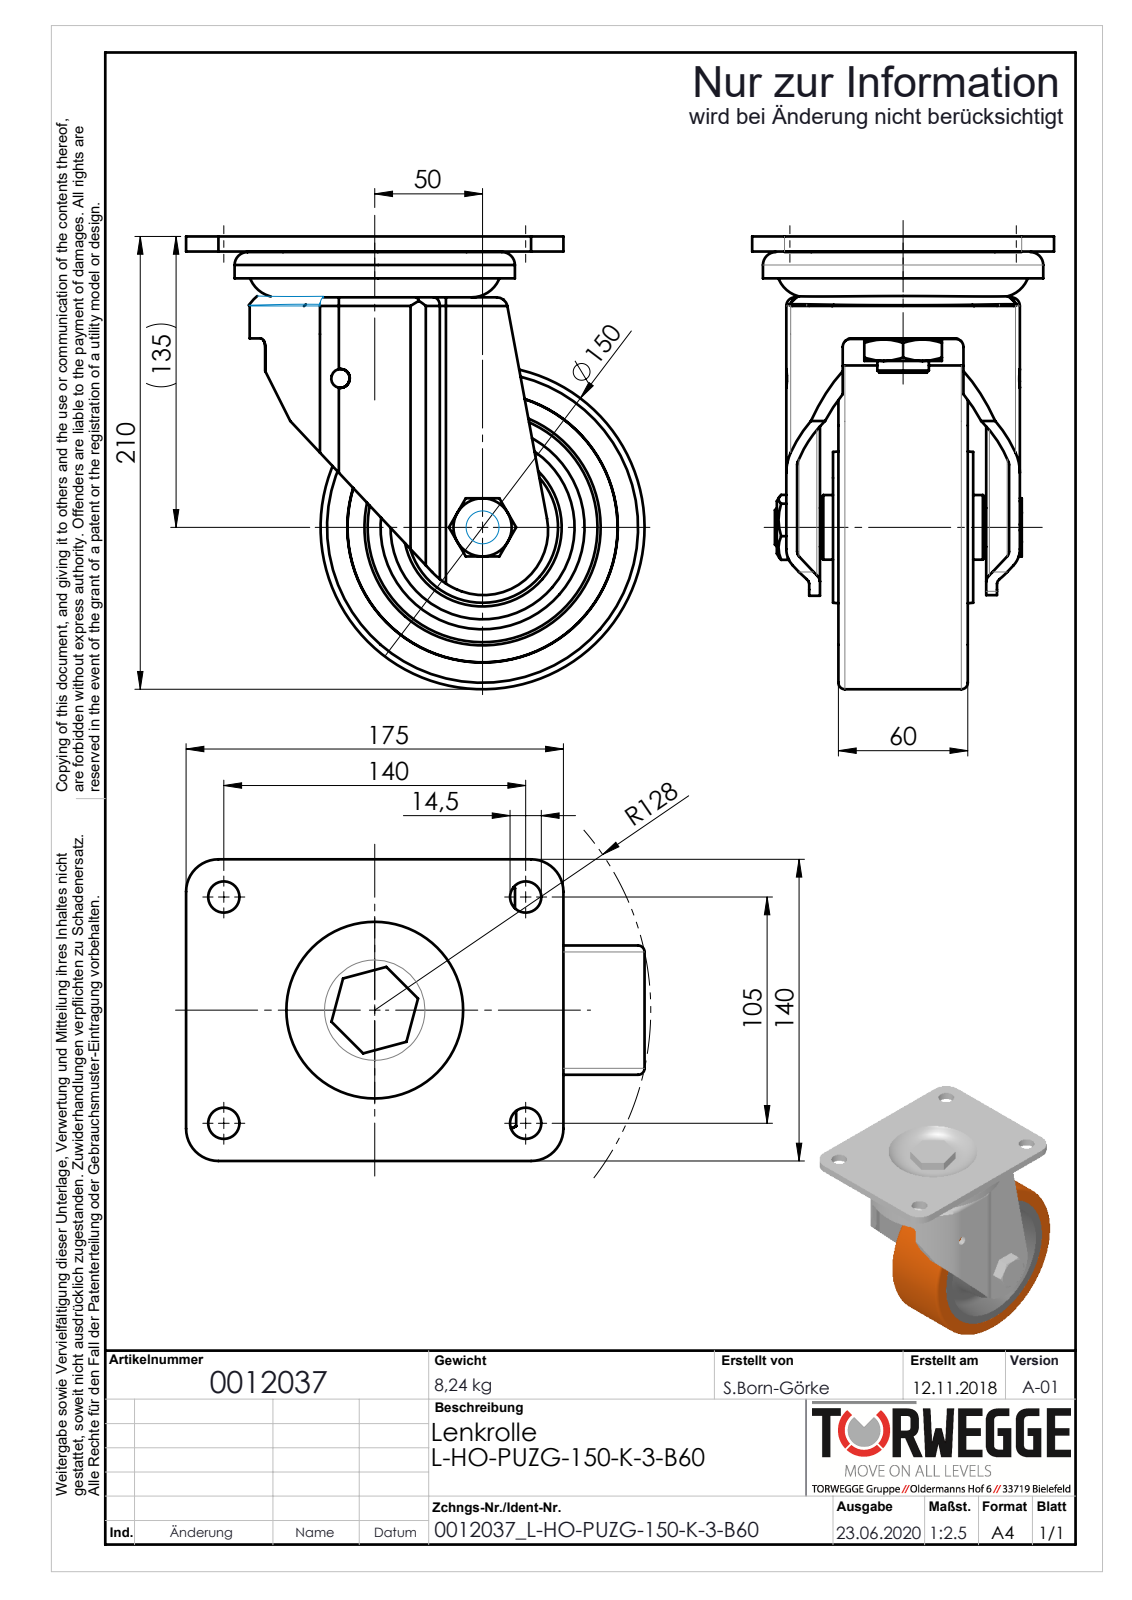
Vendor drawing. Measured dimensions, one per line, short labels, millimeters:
name: 0012037
written by: SolidWorks 2018 (AUTOMOTIVE_DESIGN)
unit: mm
bodies: 0 solids, 617 faces (133 planar, 187 cylindrical, 297 other)
size: 212.63 × 210.13 × 140
holes: 4× ⌀14.5, 2× ⌀52, 1× ⌀15.29, 1× ⌀18.3, 1× ⌀18.5, 1× ⌀24, 1× ⌀24.5, 1× ⌀24.6, 1× ⌀25, 1× ⌀26, 1× ⌀33.12, 1× ⌀40
bosses: 1× ⌀150.26, 1× ⌀130, 1× ⌀117.57, 1× ⌀90, 1× ⌀71.5, 1× ⌀60.97, 1× ⌀50, 1× ⌀36
rounds: 10× R4, 4× R4.25, 4× R15, 3× R3, 3× R5, 2× R10, 2× R20, 2× R30
face distances: 5, 7, 3.98, 4, 8, 13.55, 73.55, 10.61, 92.7, 62.5
hole spacings: 87.5, 105, 140, 175
